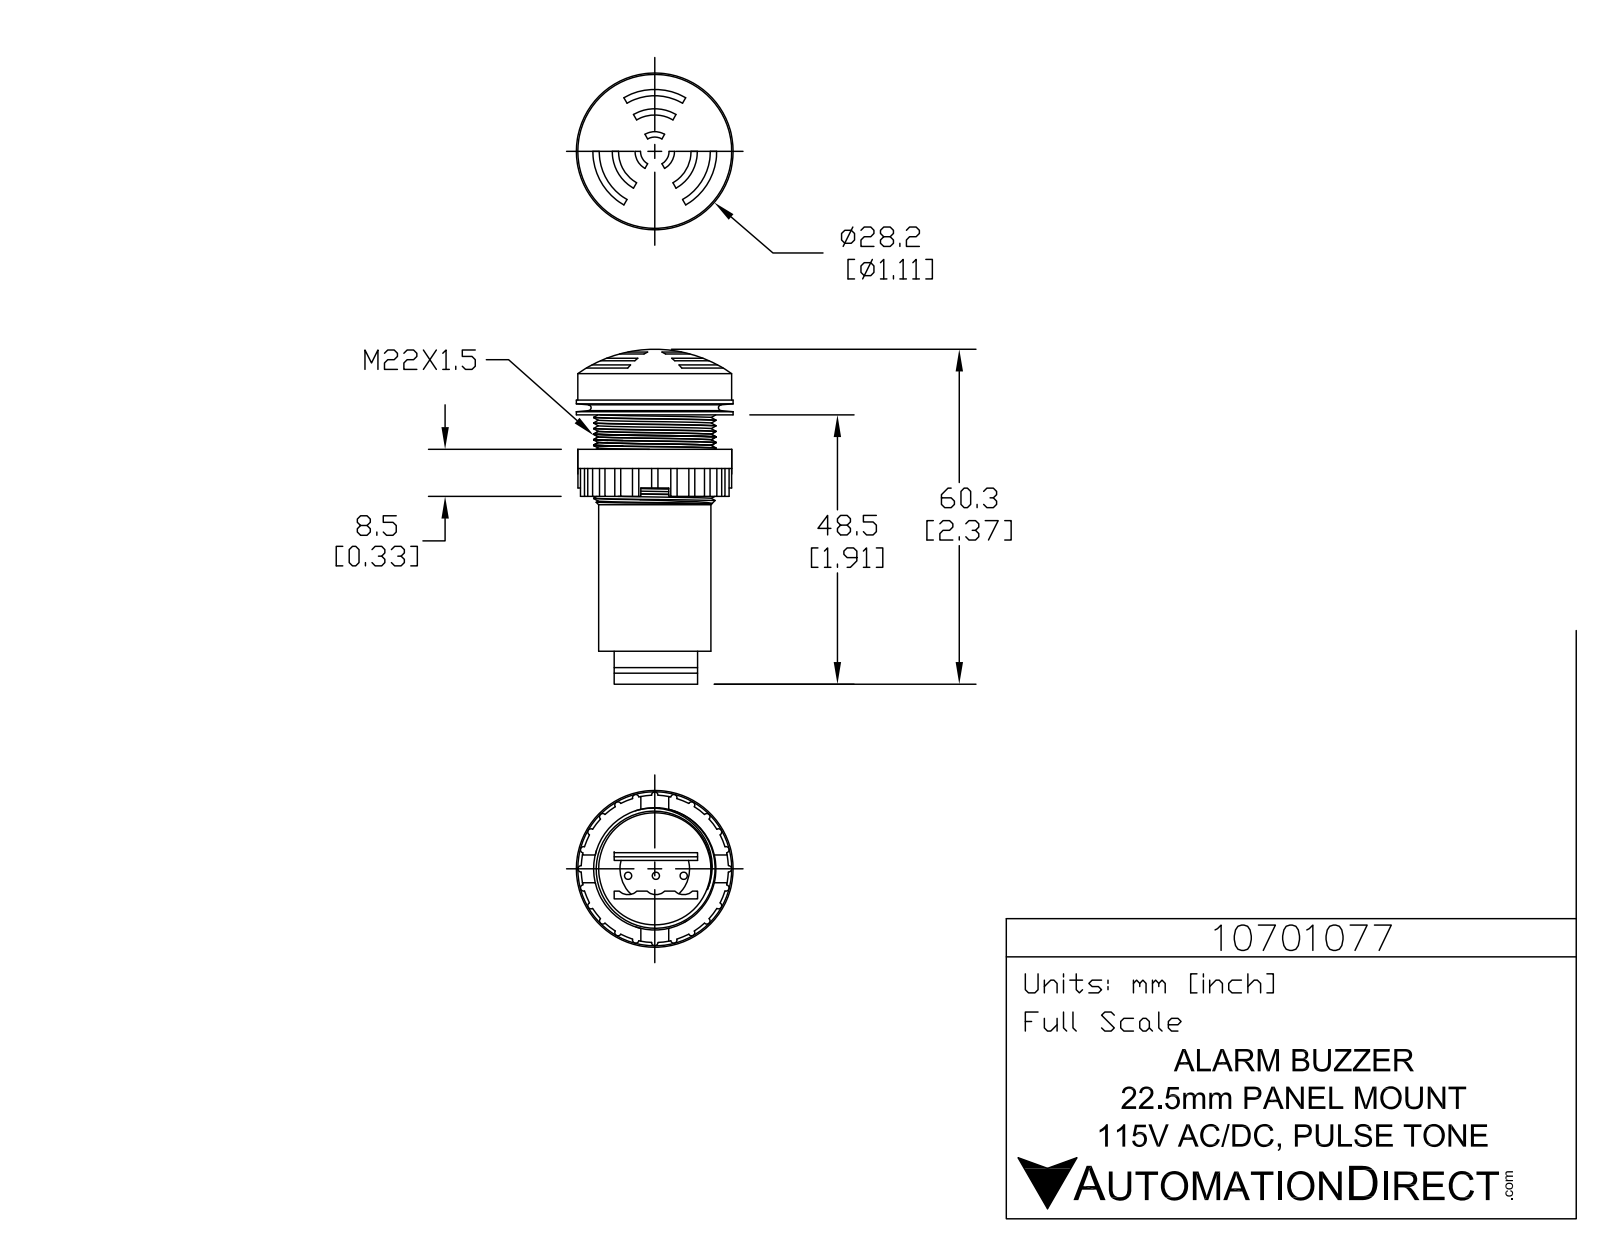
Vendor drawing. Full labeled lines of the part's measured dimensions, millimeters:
Part name (STEP PRODUCT): 10701077
STEP written by: SolidWorks 2017 (AUTOMOTIVE_DESIGN)
Units: millimetres
Bodies: 1 solid, 161 faces (37 planar, 103 cylindrical, 21 other)
Overall size (bounding box): 59.4 × 28.2 × 28.2
Volume: 21 583 mm³ · Surface area: 7 928 mm²
Round bosses / shafts (diameter × count): ⌀1.3 ×3, ⌀28.2 ×1, ⌀27.7 ×1, ⌀22 ×1, ⌀20.2 ×1
Partial cylindrical surfaces — rounded edges, fillets, slot ends (radius × count): R0.57 ×24, R2.25 ×3, R6.25 ×1, R13.25 ×1
Main face-to-face distances: 35.5, 8.5, 27, 6.9, 32.95, 3.5, 41.65, 14.65, 6.15, 2.55
